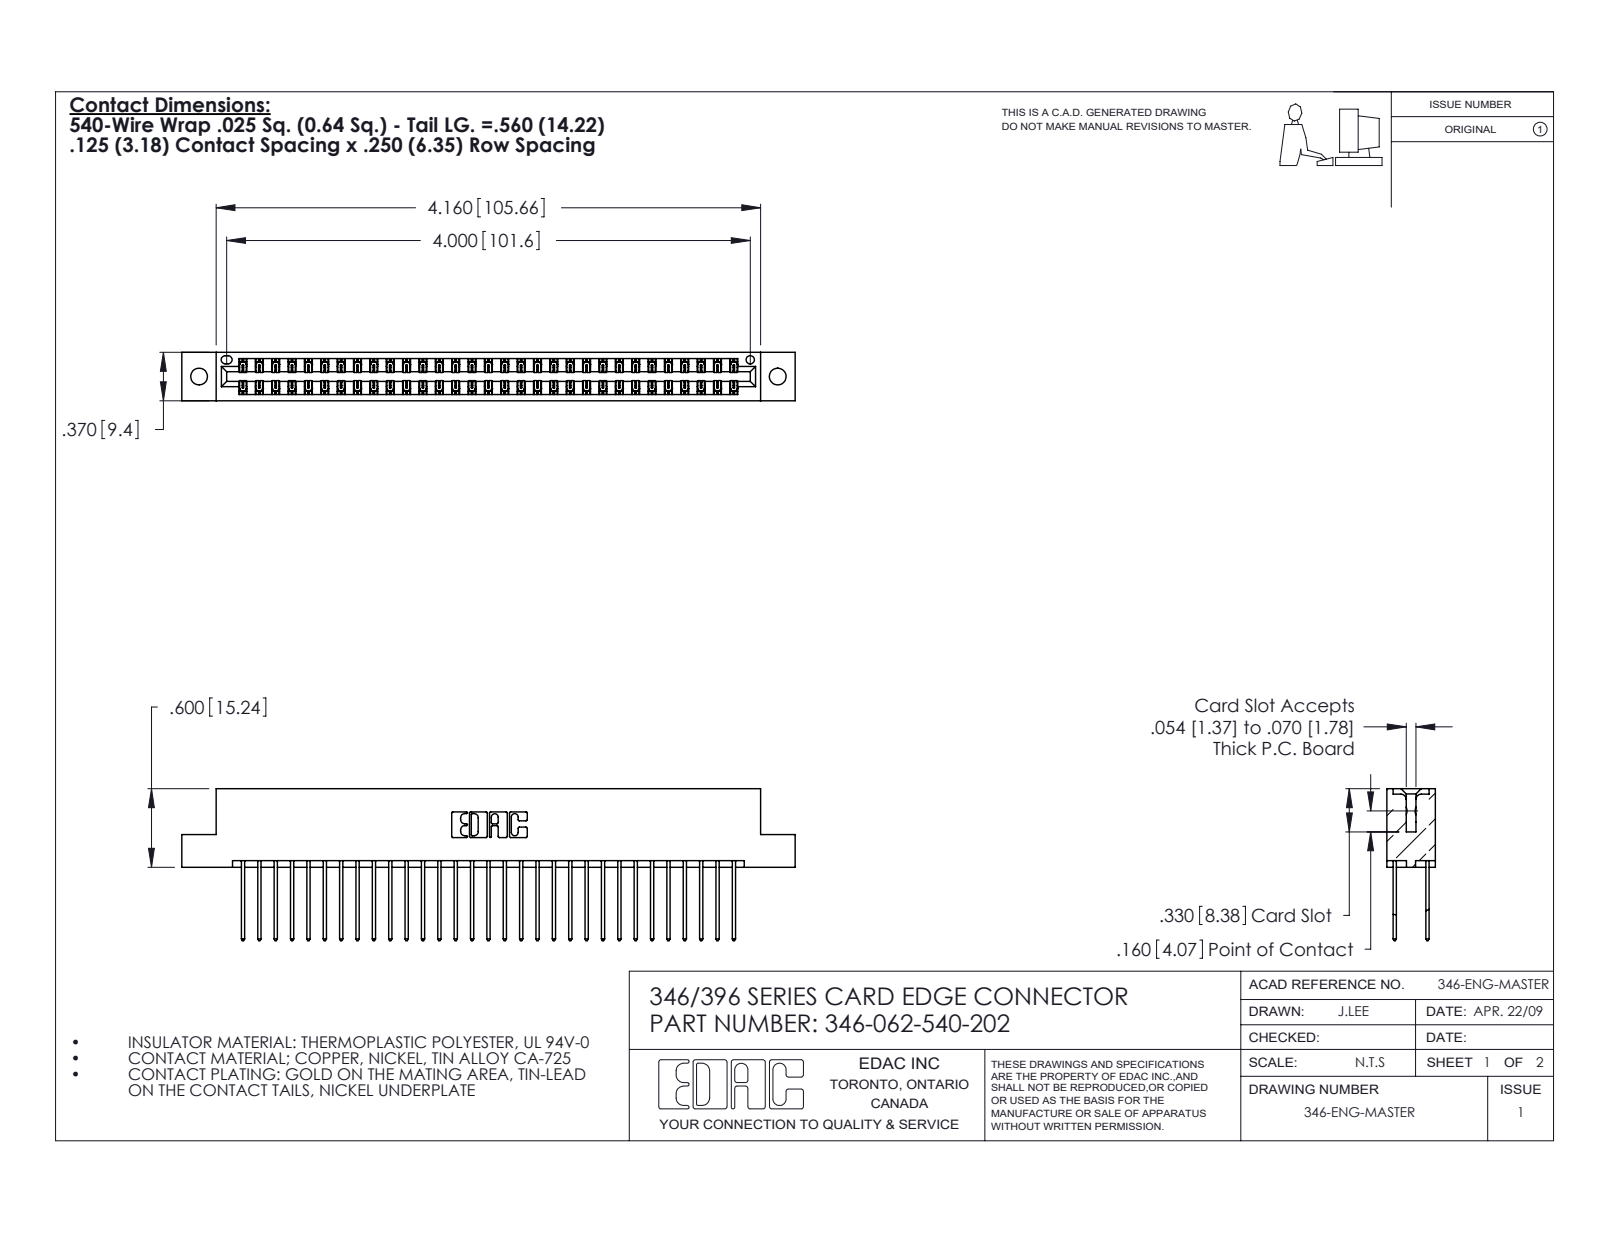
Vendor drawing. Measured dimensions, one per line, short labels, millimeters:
name: 345-292-001_345-293-140; 346 Part_Flush Mounting Lugs - 0.128 Dia; 346-062-540-202
written by: SolidWorks 2020 (CONFIG_CONTROL_DESIGN)
unit: mm
bodies: 63 solids, 3346 faces (2246 planar, 1100 cylindrical, 0 other)
size: 119 × 29.5 × 9.4
volume: 11 700 mm³; area: 16 770 mm²
holes: 2× ⌀3.3, 1× ⌀1.6
rounds: 93× R0.2, 62× R0.3, 22× R0.3, 6× R0.2, 6× R0.8, 3× R0.7, 2× R0.4, 2× R0.6
face distances: 1.2, 8.2, 6.4, 1.8, 7.6, 0.6, 9.4, 7, 3.8, 5.6
hole spacings: 6.2, 107, 112.3
